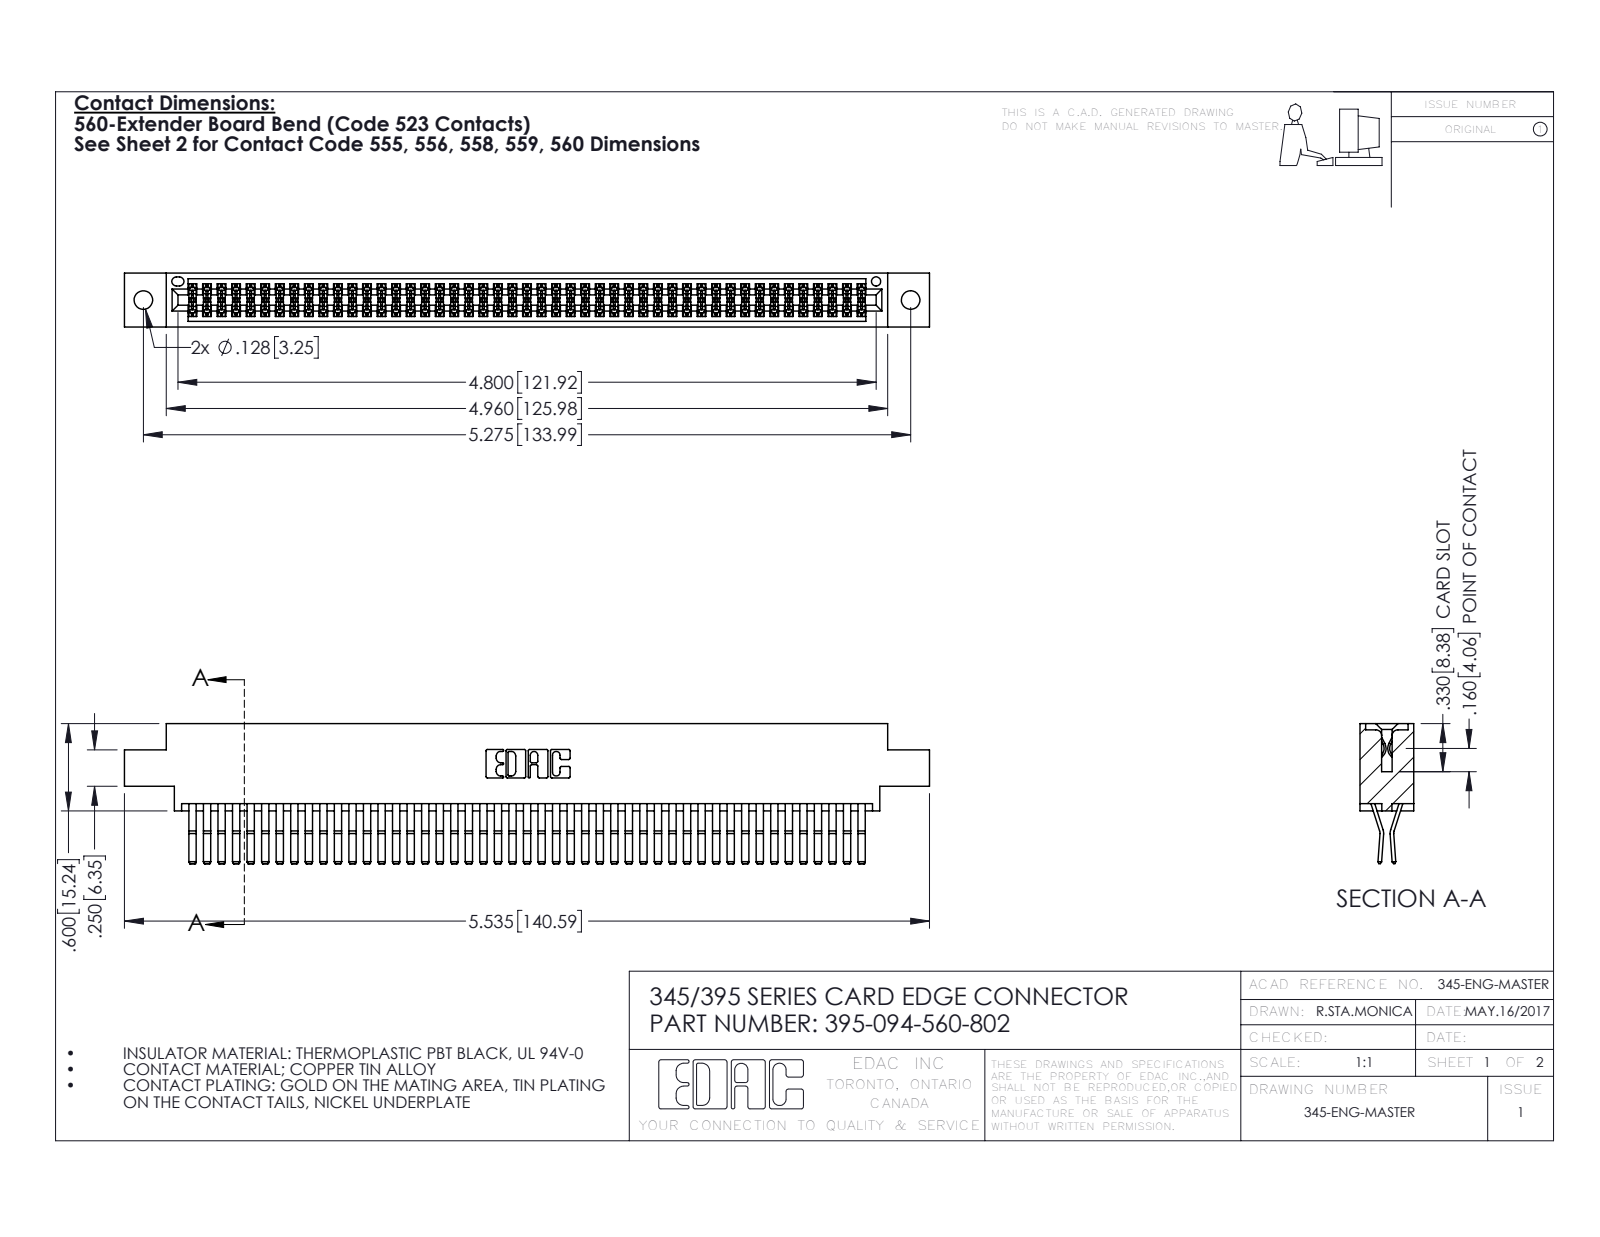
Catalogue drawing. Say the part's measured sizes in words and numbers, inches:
The part is named "345 Part_0.170 Offset - 0.128 Dia; 395-094-560-802; 345-292-001_560 Tail". Its 3-D file was written by "SolidWorks 2016 (CONFIG_CONTROL_DESIGN)". It is 95 solids with 5018 faces: 3186 planar, 1832 cylindrical and 0 other. Overall it measures 5.535 by 0.962 by 0.37 inches. Its volume is 0.865 cubic inches and its surface area 34.87 square inches. Round holes: 2 of diameter 0.128, 1 of diameter 0.064. Partial cylindrical surfaces (rounded edges, fillets, slot ends): 141 of radius 0.006, 22 of radius 0.01, 6 of radius 0.007, 6 of radius 0.031, 3 of radius 0.026, 2 of radius 0.01, 2 of radius 0.014, 2 of radius 0.019. The main face-to-face distances are 0.025, 0.298, 0.072, 0.37, 0.2, 0.098, 0.272, 0.225, 0.175, 0.149. The hole center spacings are 0.27, 5.039, 5.275.
